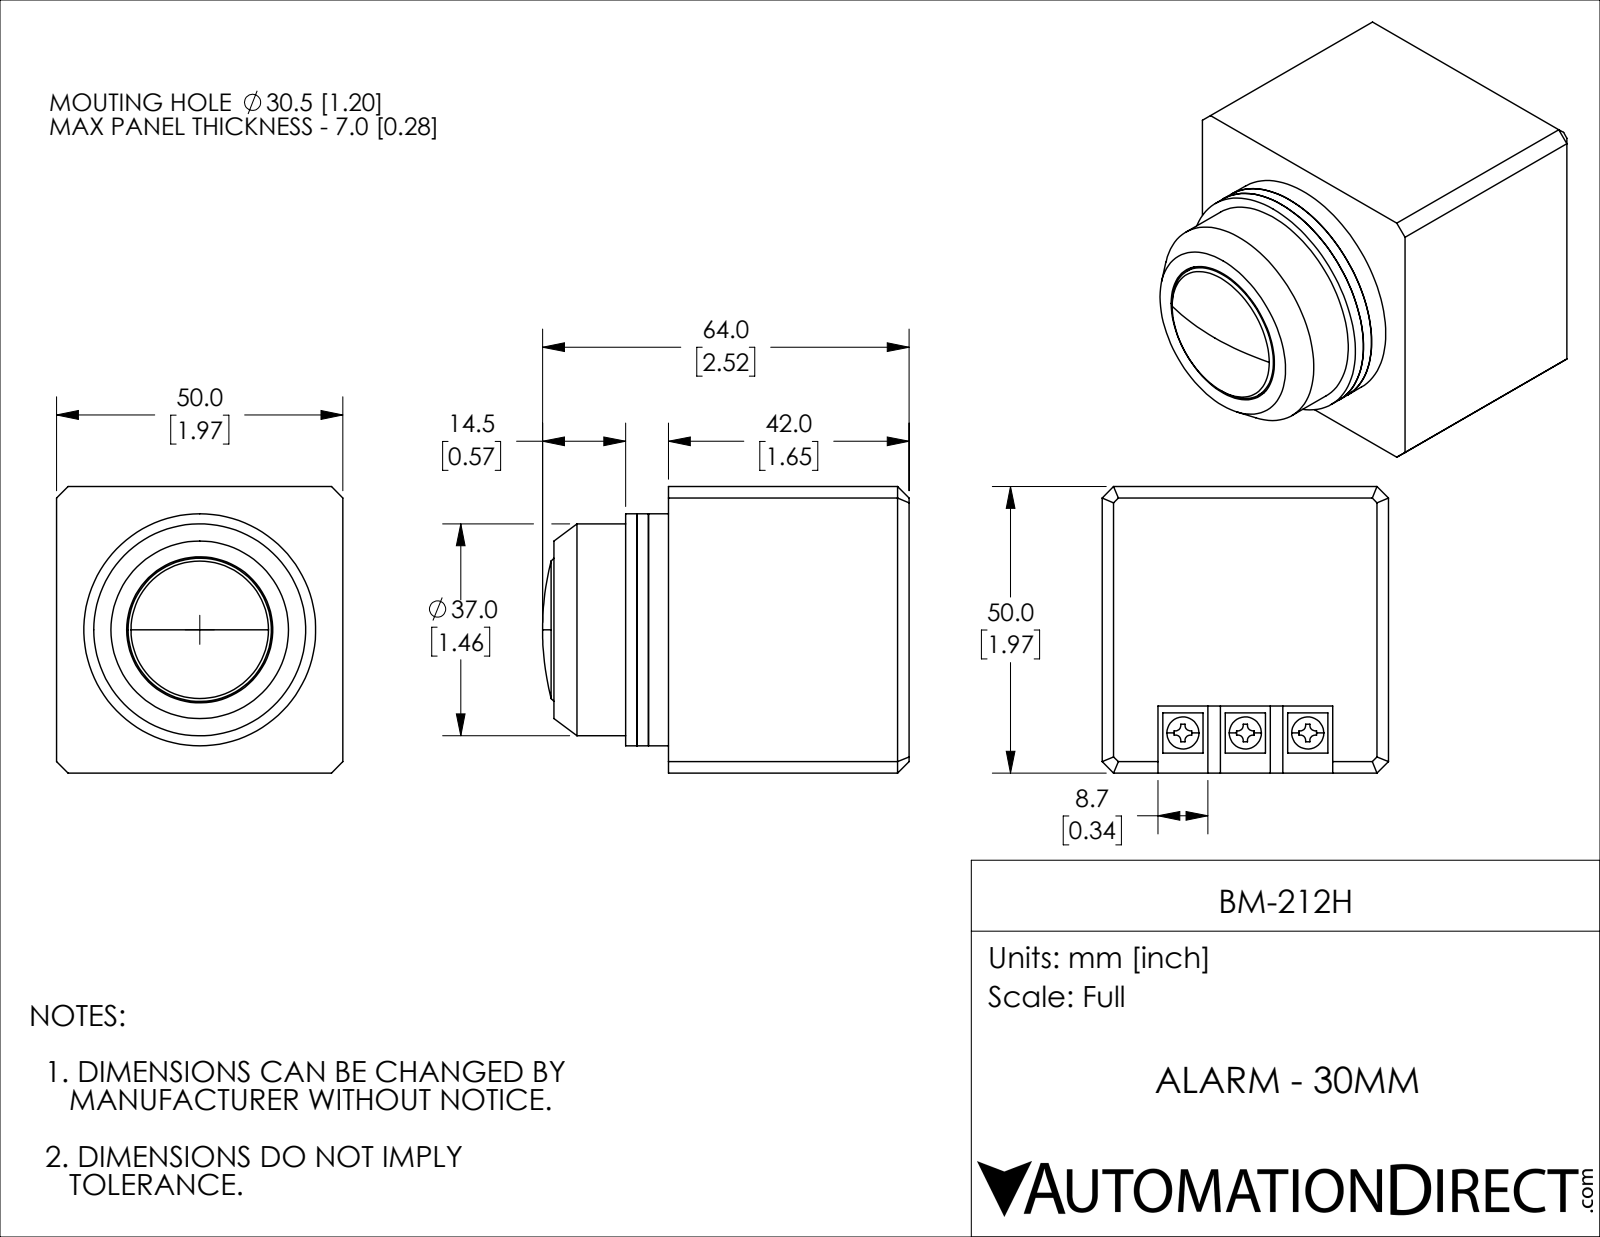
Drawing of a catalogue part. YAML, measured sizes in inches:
part_name: "BM-212H"
step_written_by: "SolidWorks 2018 (AUTOMOTIVE_DESIGN)"
units: inches
bodies: {solids: 5, faces: 120, planar: 68, cylindrical: 22, other: 30}
overall_size: [2.52, 1.969, 1.969]
volume: 7.482
surface_area: 37.72
round_holes:
  - {diameter: 1.004, count: 1}
  - {diameter: 1.181, count: 1}
  - {diameter: 1.201, count: 1}
round_bosses_or_shafts:
  - {diameter: 1.594, count: 1}
  - {diameter: 1.457, count: 1}
  - {diameter: 0.984, count: 1}
face_to_face_distances: [1.969, 0.079, 1.654, 1.791, 0.157, 0.138, 0.217, 1.87, 0.295, 1.949]
